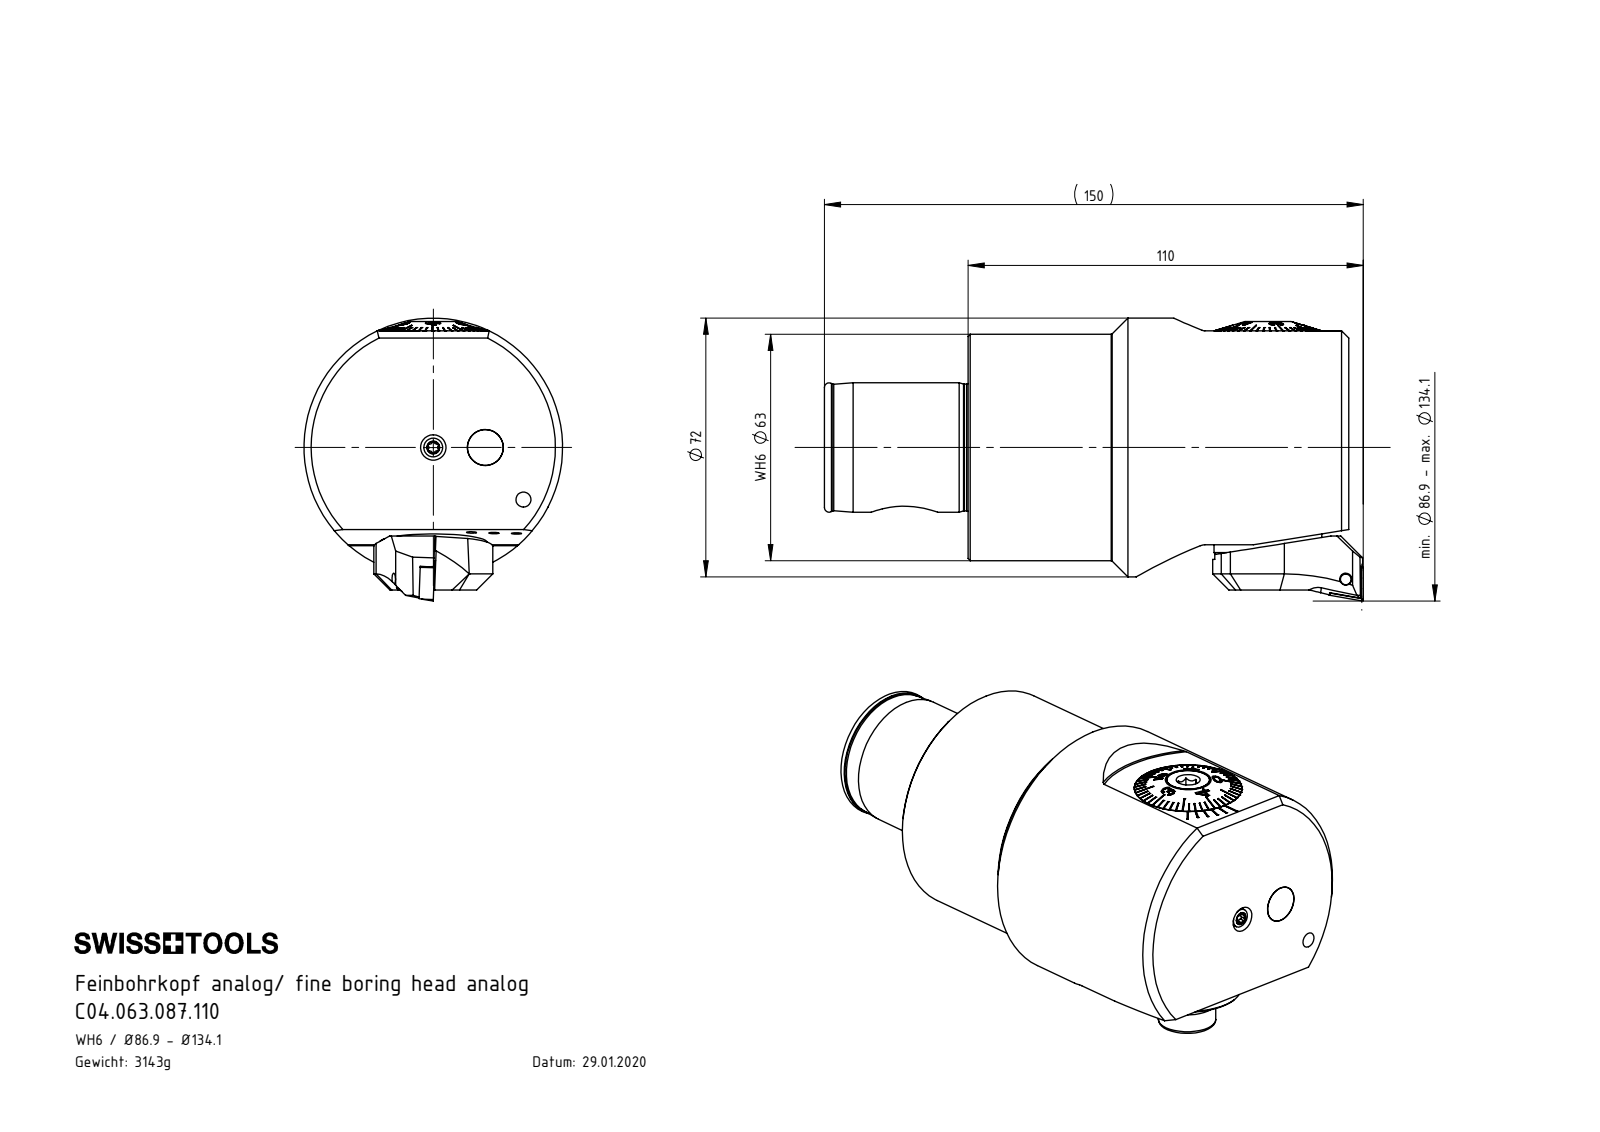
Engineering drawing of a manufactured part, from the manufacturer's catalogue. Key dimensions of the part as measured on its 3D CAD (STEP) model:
Part name (STEP PRODUCT): A55-BG2.013.005_C; A55-BG2.012.006_B; F72-BG2.014.020_B; F72-BG2.015.020_B (+8 more)
STEP written by: SolidWorks 2017 (CONFIG_CONTROL_DESIGN)
Units: millimetres
Bodies: 18 solids, 866 faces (338 planar, 174 cylindrical, 354 other)
Overall size (bounding box): 150 × 78.89 × 72
Volume: 440 557 mm³ · Surface area: 70 044 mm²
Round holes (diameter × count): ⌀3.3 ×9, ⌀8.5 ×2, ⌀12 ×2, ⌀4.2 ×1, ⌀4.4 ×1, ⌀5 ×1, ⌀6.1 ×1, ⌀8 ×1, ⌀10 ×1, ⌀11 ×1, ⌀11.75 ×1, ⌀12.4 ×1
Round bosses / shafts (diameter × count): ⌀10 ×2, ⌀5.25 ×2, ⌀4 ×2, ⌀72 ×1, ⌀63 ×1, ⌀36 ×1, ⌀35.3 ×1, ⌀29.98 ×1
Partial cylindrical surfaces — rounded edges, fillets, slot ends (radius × count): R0.34 ×12, R0.59 ×12, R0.5 ×4, R3.2 ×3, R10 ×2, R1 ×1, R1.65 ×1, R3.5 ×1
Main face-to-face distances: 106, 55.8, 40, 146, 2.5, 62.28, 6.48, 61.1, 5.3, 1.18
Hole centre spacings: 5.73, 5.86, 14.05, 14.5, 26, 32.5
